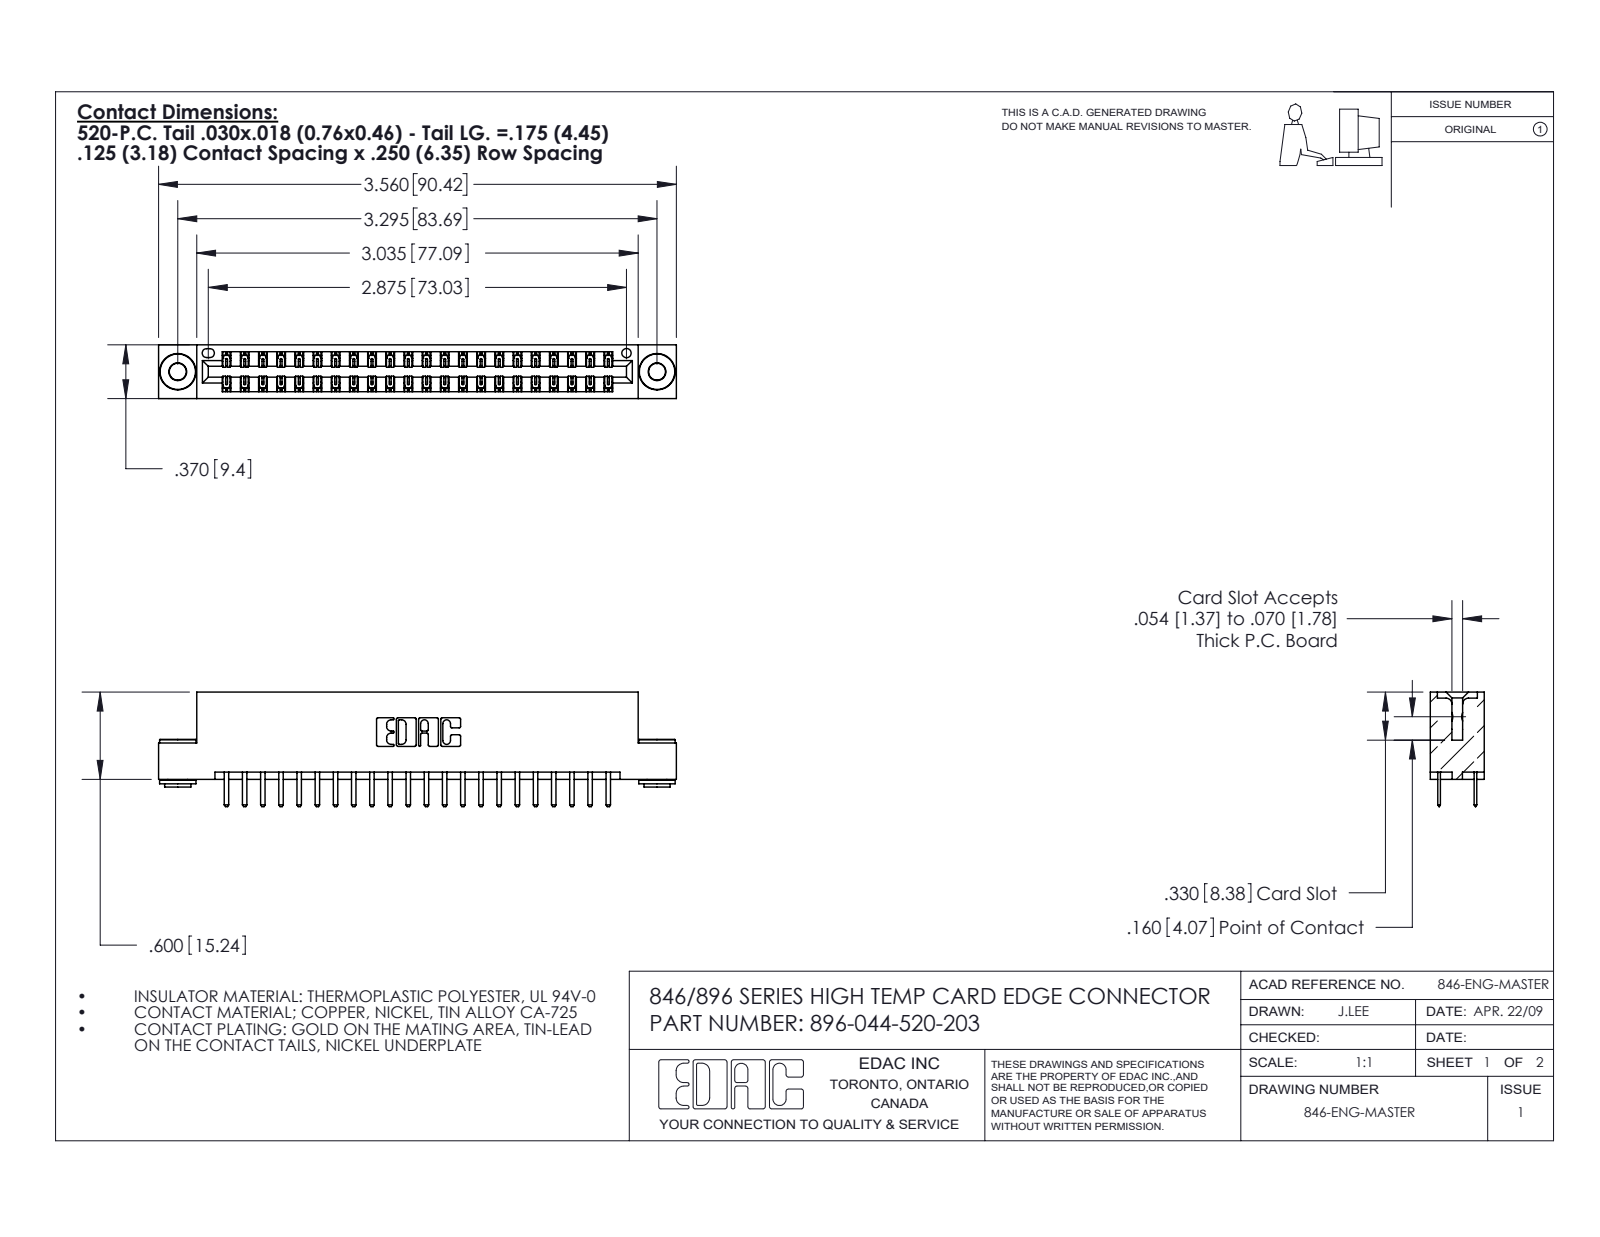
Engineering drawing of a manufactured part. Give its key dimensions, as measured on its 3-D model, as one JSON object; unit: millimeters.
{"part_name": "396-044-520-203; 346 Part_Flush Mounting Lugs - 0.156 Dia-TH; 345-292-001_345-293-120; 345-250-002_345-250-002-102", "step_written_by": "SolidWorks 2016 (CONFIG_CONTROL_DESIGN)", "units": "millimeters", "bodies": {"solids": 47, "faces": 2624, "planar": 1714, "cylindrical": 902, "other": 8}, "overall_size": [90.4, 20, 9.4], "volume_mm3": 8670, "surface_area_mm2": 11760, "round_holes": [[2.9, 2], [4, 2], [1.6, 1]], "round_bosses_or_shafts": [[6.4, 2], [4.6, 2], [3.5, 2]], "partial_cylinders_radius": [[0.2, 66], [0.3, 48], [0.3, 22], [0.2, 6], [0.8, 6], [0.7, 3], [0.4, 2], [0.6, 2]], "face_to_face_distances": [6.4, 1.2, 8.2, 9.4, 0.6, 7, 1.8, 7.6, 3.8, 5.6], "hole_center_spacings": [6.2, 78.4, 83.7]}
